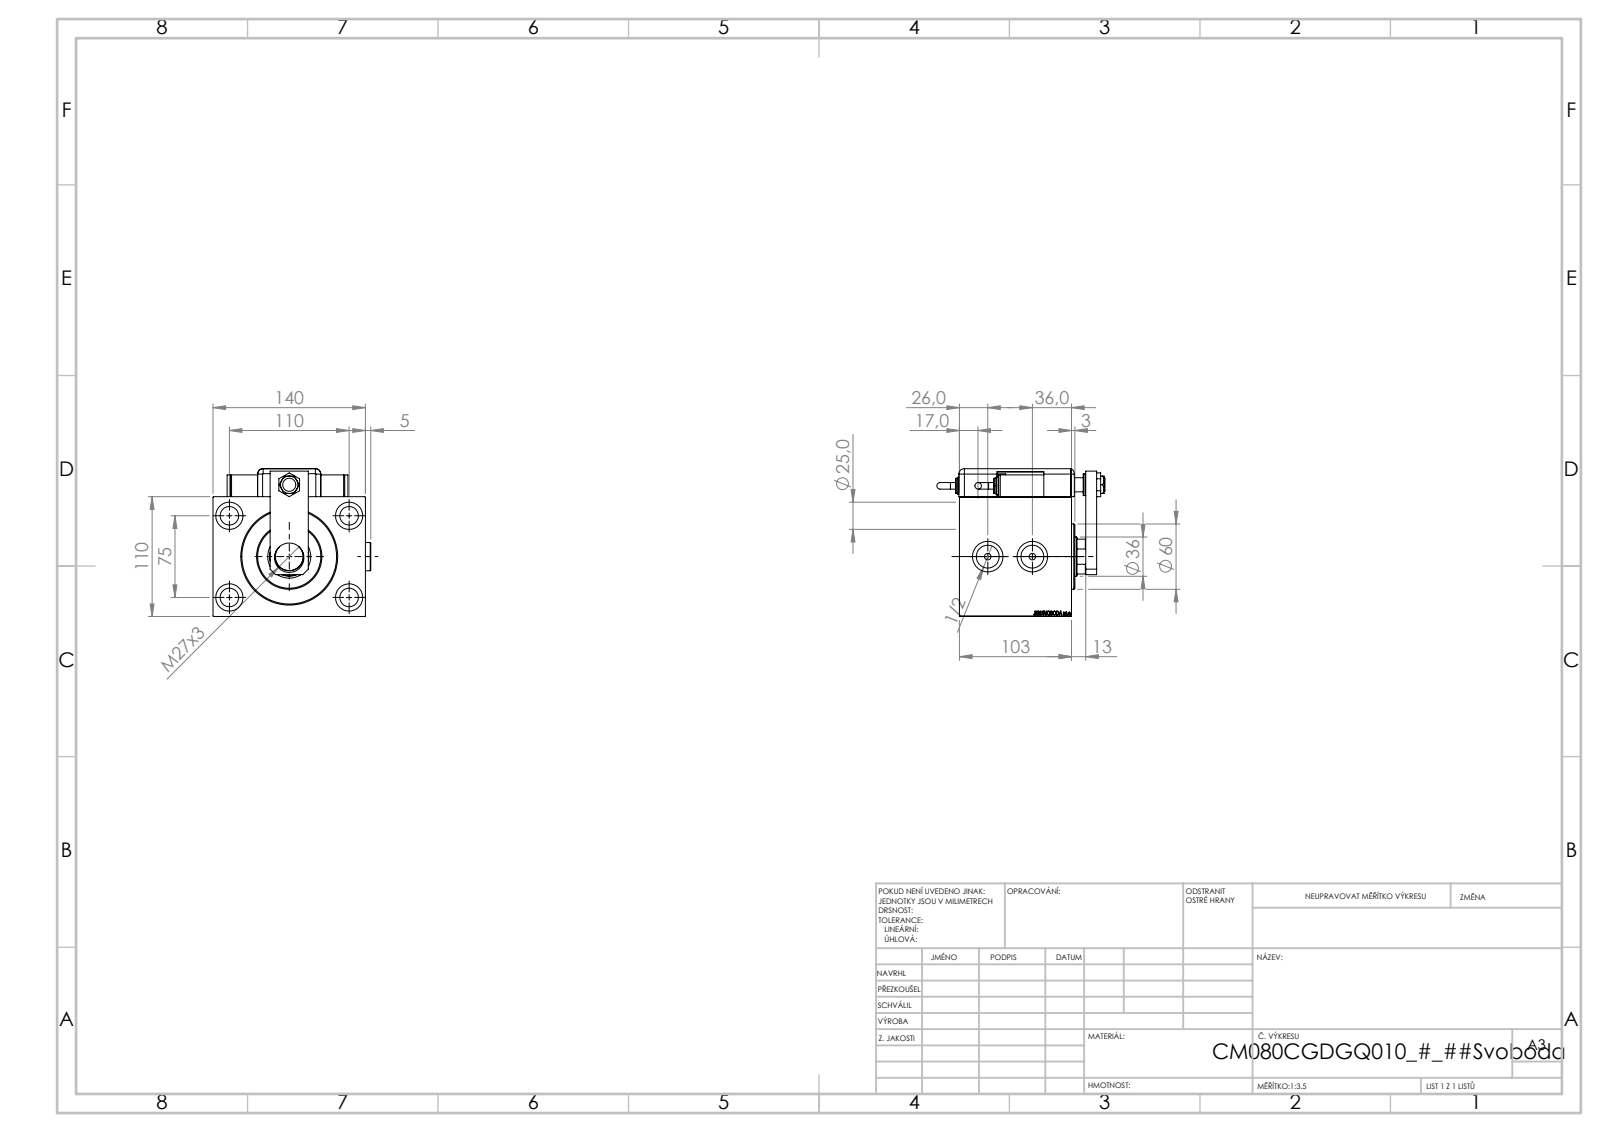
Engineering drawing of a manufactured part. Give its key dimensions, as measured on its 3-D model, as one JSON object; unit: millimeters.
{"part_name": "MAGNETIC SWITCH Q; V450CM_C_VCP; V450CM_VC_B; TYC (+7 more)", "step_written_by": "SolidWorks 2019 (CONFIG_CONTROL_DESIGN)", "units": "millimeters", "bodies": {"solids": 15, "faces": 1301, "planar": 649, "cylindrical": 131, "other": 521}, "overall_size": [154.46, 144.9, 135.8], "volume_mm3": 1553000, "surface_area_mm2": 227320, "round_holes": [[17, 4], [25, 4], [4, 2], [6, 2], [8, 2], [20.96, 2], [28, 2], [12, 1], [13, 1], [14, 1], [25.5, 1], [27, 1]], "round_bosses_or_shafts": [[20, 3], [26, 2], [16, 2], [14, 2], [6, 2], [60, 1]], "partial_cylinders_radius": [[5, 9], [10, 1], [17.5, 1]], "face_to_face_distances": [110, 103, 52, 3, 51, 140, 10, 44.6, 20, 13], "hole_center_spacings": [66.57, 61.95, 66.01, 67.14, 75, 110, 117.21, 133.14]}
